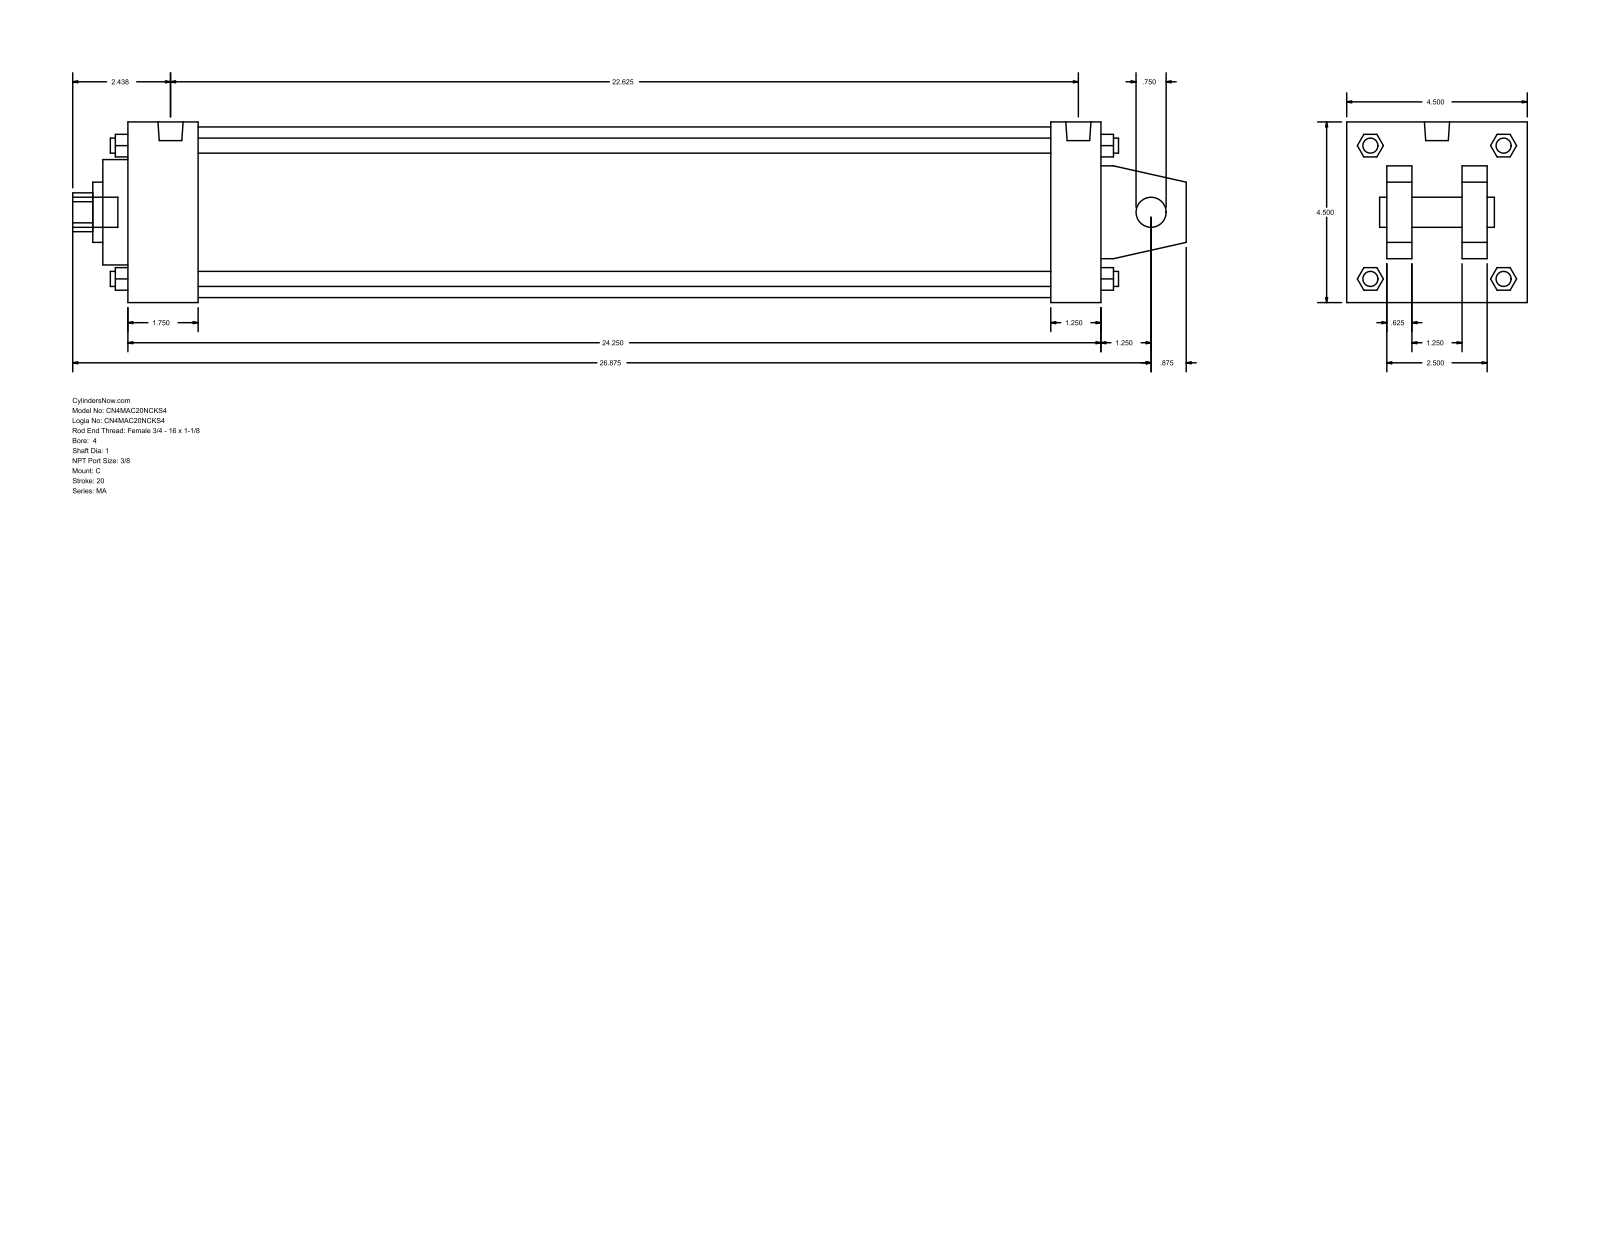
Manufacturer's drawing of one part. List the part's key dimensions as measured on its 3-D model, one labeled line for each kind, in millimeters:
Part name (STEP PRODUCT): MA_C__0400_1
STEP written by: GSSL Pune (CONFIG_CONTROL_DESIGN)
Units: millimetres
Bodies: 0 solids, 141 faces (109 planar, 32 cylindrical, 0 other)
Overall size (bounding box): 704.85 × 114.3 × 114.3
Round holes (diameter × count): ⌀19.05 ×1, ⌀25.4 ×1, ⌀38.1 ×1, ⌀66.67 ×1, ⌀107.95 ×1
Round bosses / shafts (diameter × count): ⌀11.11 ×4, ⌀9.53 ×4, ⌀15.93 ×2, ⌀19.05 ×1
Partial cylindrical surfaces — rounded edges, fillets, slot ends (radius × count): R12.29 ×1
Main face-to-face distances: 114.3, 615.96, 15.87, 31.76, 73.03, 41.27, 25.4, 88.9, 47.63, 584.2
